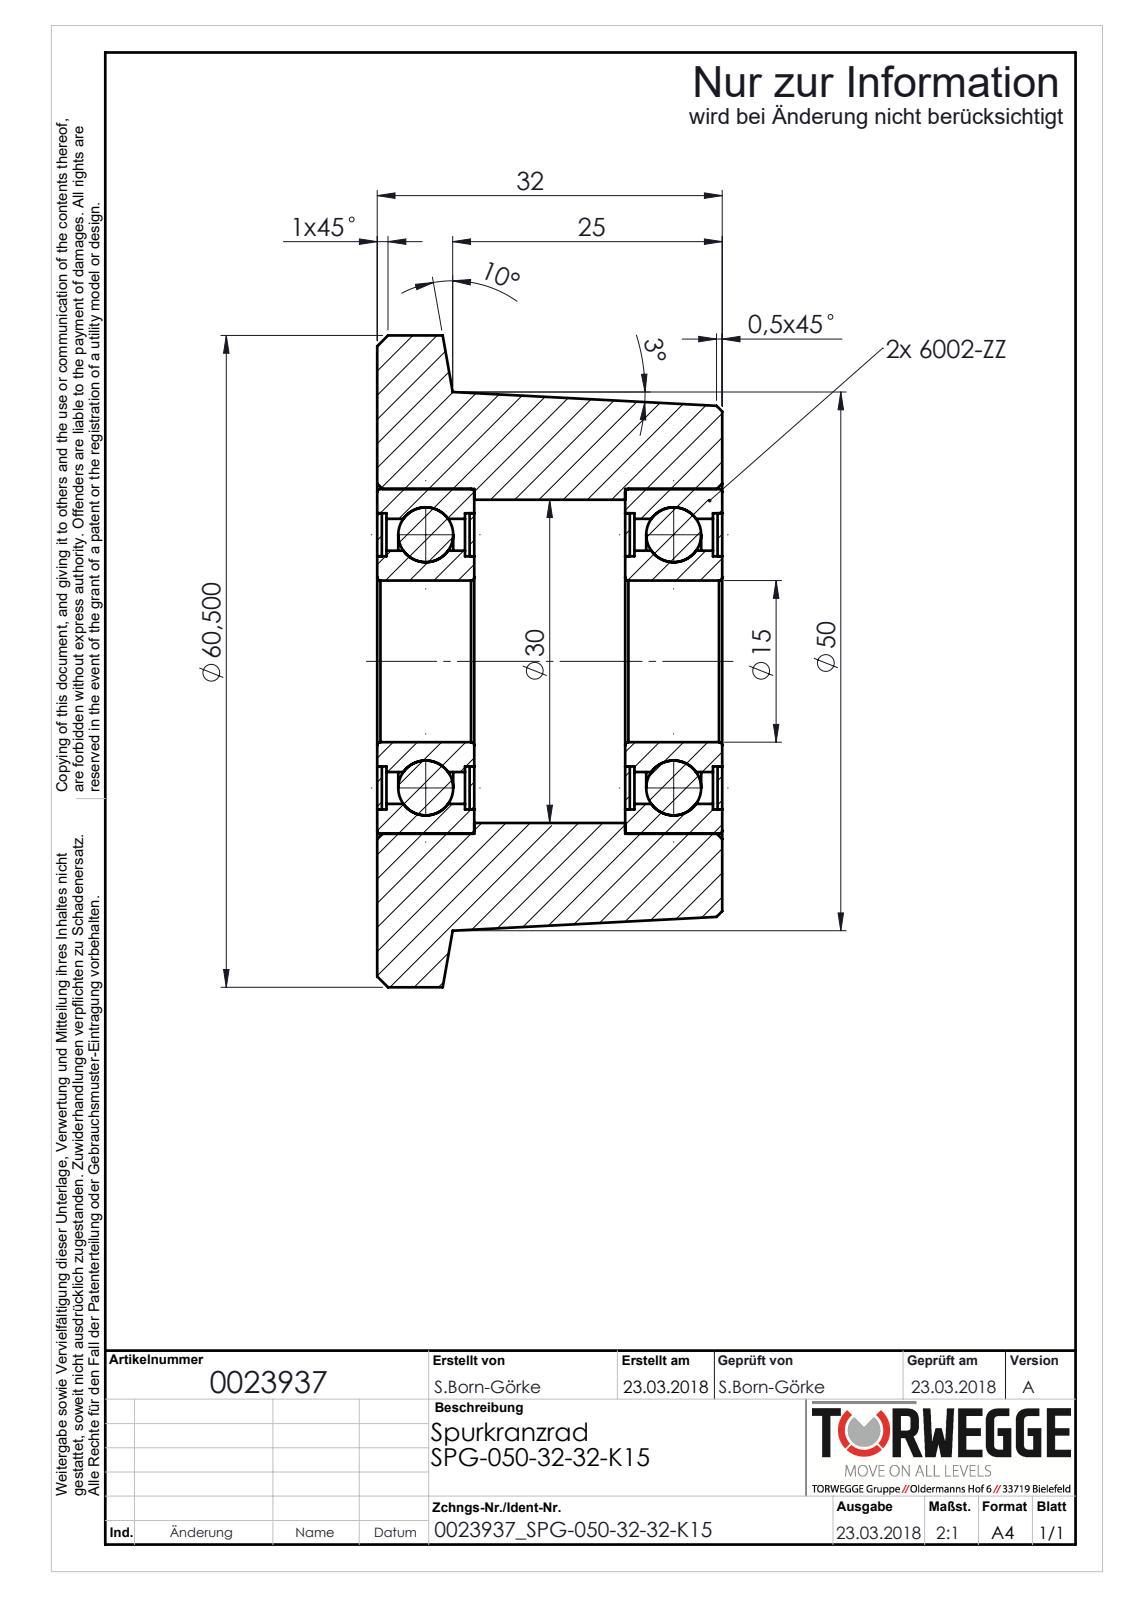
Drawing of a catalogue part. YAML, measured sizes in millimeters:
part_name: "SPG-TF_0017431_SPG-050-32-32-KS32x9; 0017525_Rillenkugellager_DIN625-6002-15-ZZ; 0023937_SPG-050-32-32-K15"
step_written_by: "SolidWorks 2018 (AUTOMOTIVE_DESIGN)"
units: millimeters
bodies: {solids: 11, faces: 140, planar: 28, cylindrical: 64, other: 48}
overall_size: [60.5, 60.5, 32]
volume: 51429
surface_area: 24111
round_holes:
  - {diameter: 15, count: 1}
  - {diameter: 19.5, count: 1}
  - {diameter: 26.46, count: 1}
  - {diameter: 27.5, count: 1}
  - {diameter: 30, count: 1}
  - {diameter: 32, count: 1}
round_bosses_or_shafts:
  - {diameter: 60.5, count: 1}
  - {diameter: 20.54, count: 1}
face_to_face_distances: [23, 0.43, 32, 9, 8.57, 8.14, 22.57, 23.43, 14, 31.57]
